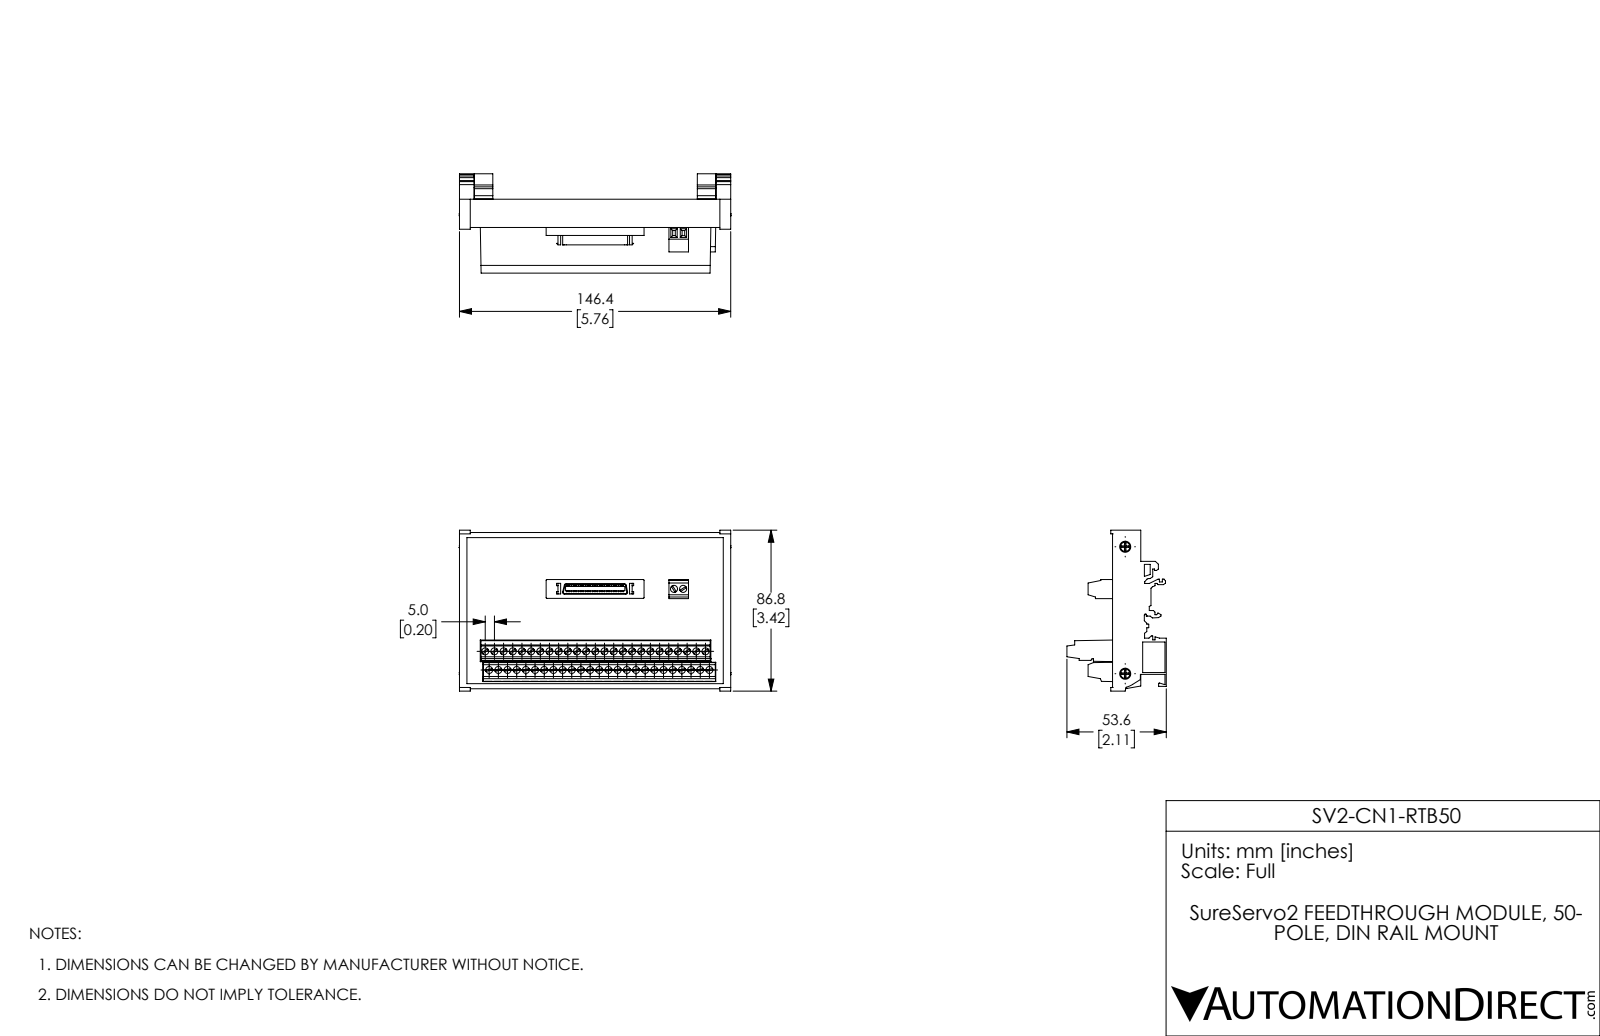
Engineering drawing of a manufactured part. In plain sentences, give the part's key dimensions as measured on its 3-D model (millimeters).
The part is named "SV2-CN1-RTB50". Its 3-D file was written by "SolidWorks 2017 (AUTOMOTIVE_DESIGN)". It is 3 solids with 1418 faces: 1261 planar, 153 cylindrical and 4 other. Overall it measures 146.73 by 86.8 by 53.61 millimeters. Its volume is 228 579 cubic millimeters and its surface area 55 754 square millimeters. Round holes: 50 of diameter 3.76, 2 of diameter 3.81, 1 of diameter 5.97, 1 of diameter 5.97. Round bosses or shafts: 2 of diameter 5.08. Partial cylindrical surfaces (rounded edges, fillets, slot ends): 10 of radius 0.38, 4 of radius 0.64, 4 of radius 1.02, 2 of radius 12.7, 1 of radius 0.35, 1 of radius 0.64, 1 of radius 1.63. The main face-to-face distances are 14.48, 146.4, 12, 0.76, 15.24, 1, 13.73, 28.21, 28.97, 0.68. The hole center spacings are 4.95, 14.86, 19.81, 29.72, 34.67, 49.53, 9.91, 44.58.
